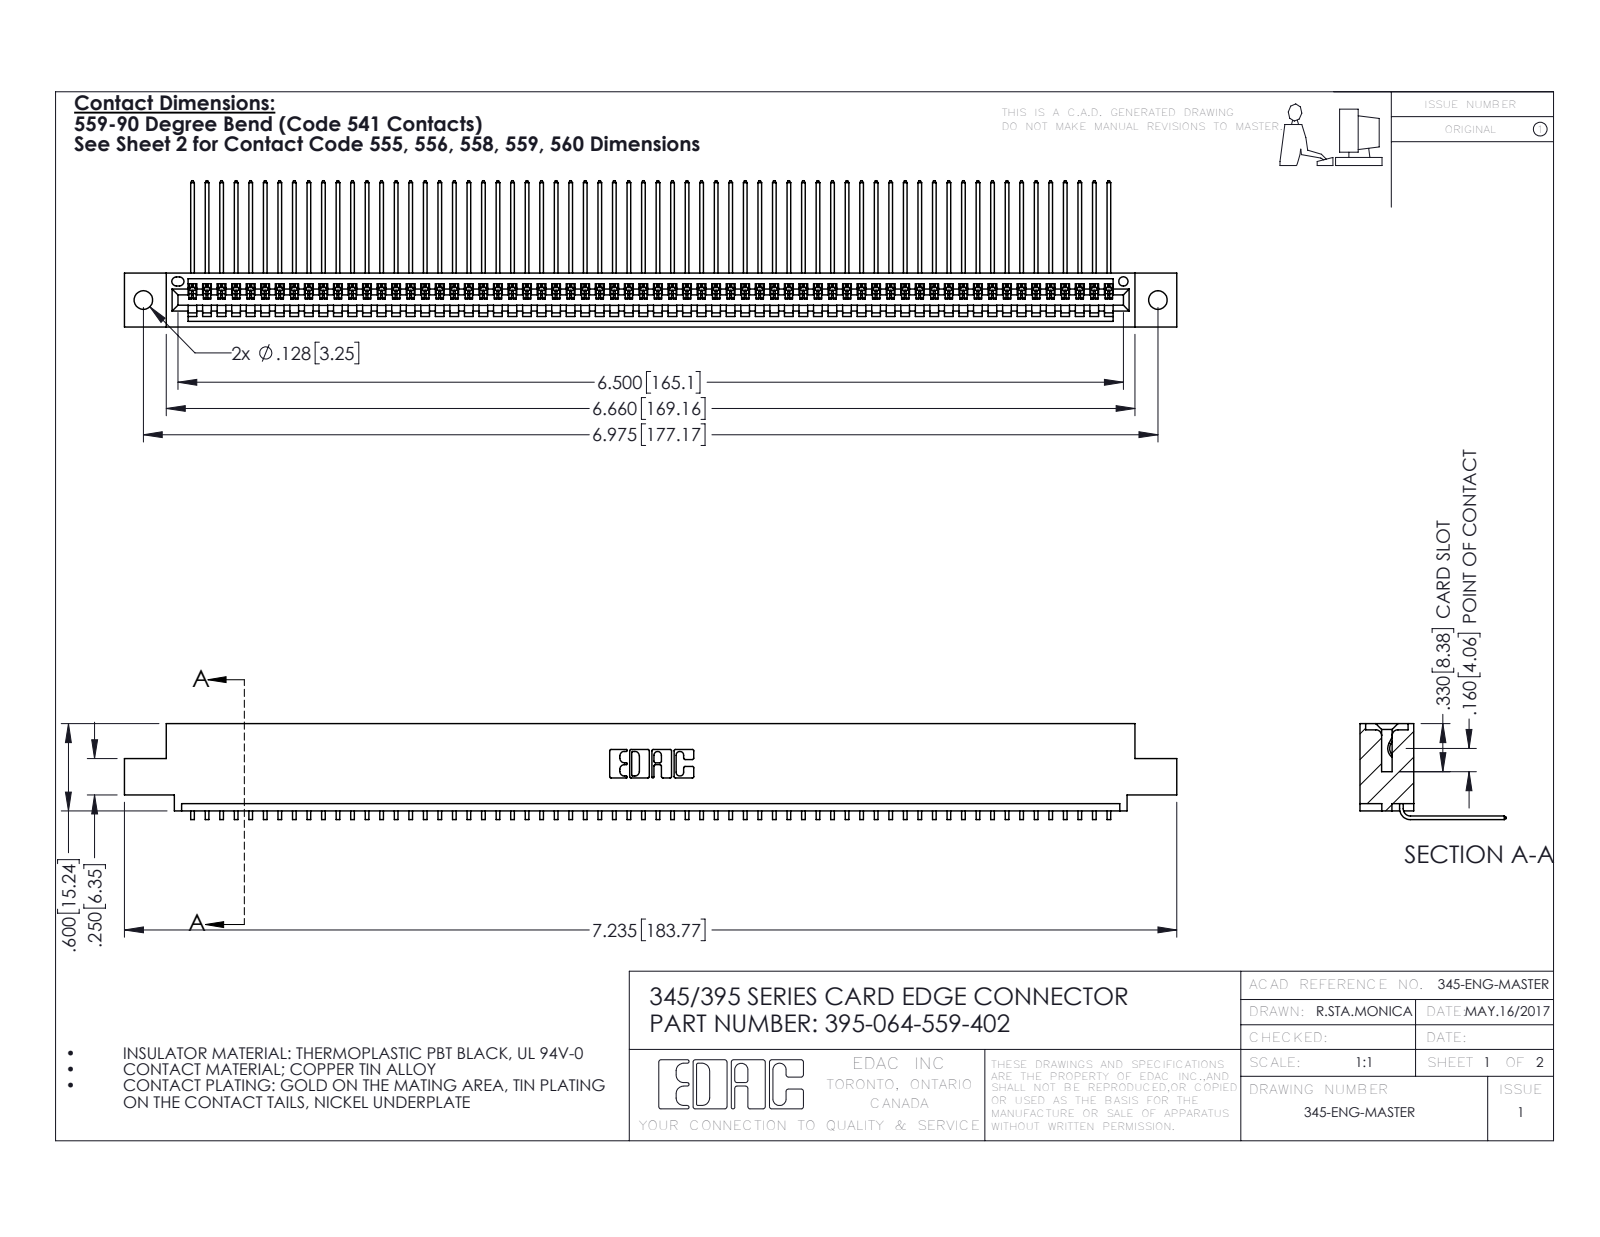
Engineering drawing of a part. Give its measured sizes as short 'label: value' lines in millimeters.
name: 395-064-559-402; 345 Part_0.110 Offset - 0.128 Dia; 345-292-001_558 559 Tail - 1
written by: SolidWorks 2016 (CONFIG_CONTROL_DESIGN)
unit: mm
bodies: 65 solids, 3970 faces (2772 planar, 1198 cylindrical, 0 other)
size: 183.8 × 25.5 × 16.7
volume: 17 730 mm³; area: 24 940 mm²
holes: 2× ⌀3.3, 1× ⌀1.6
rounds: 128× R0.2, 22× R0.3, 6× R0.2, 6× R0.8, 3× R0.7, 2× R0.8, 2× R1, 1× R0.4
face distances: 1.8, 7.6, 9.4, 5.1, 2.5, 6.9, 0.6, 5.7, 3.8, 1.8
hole spacings: 6.9, 171.2, 177.2
